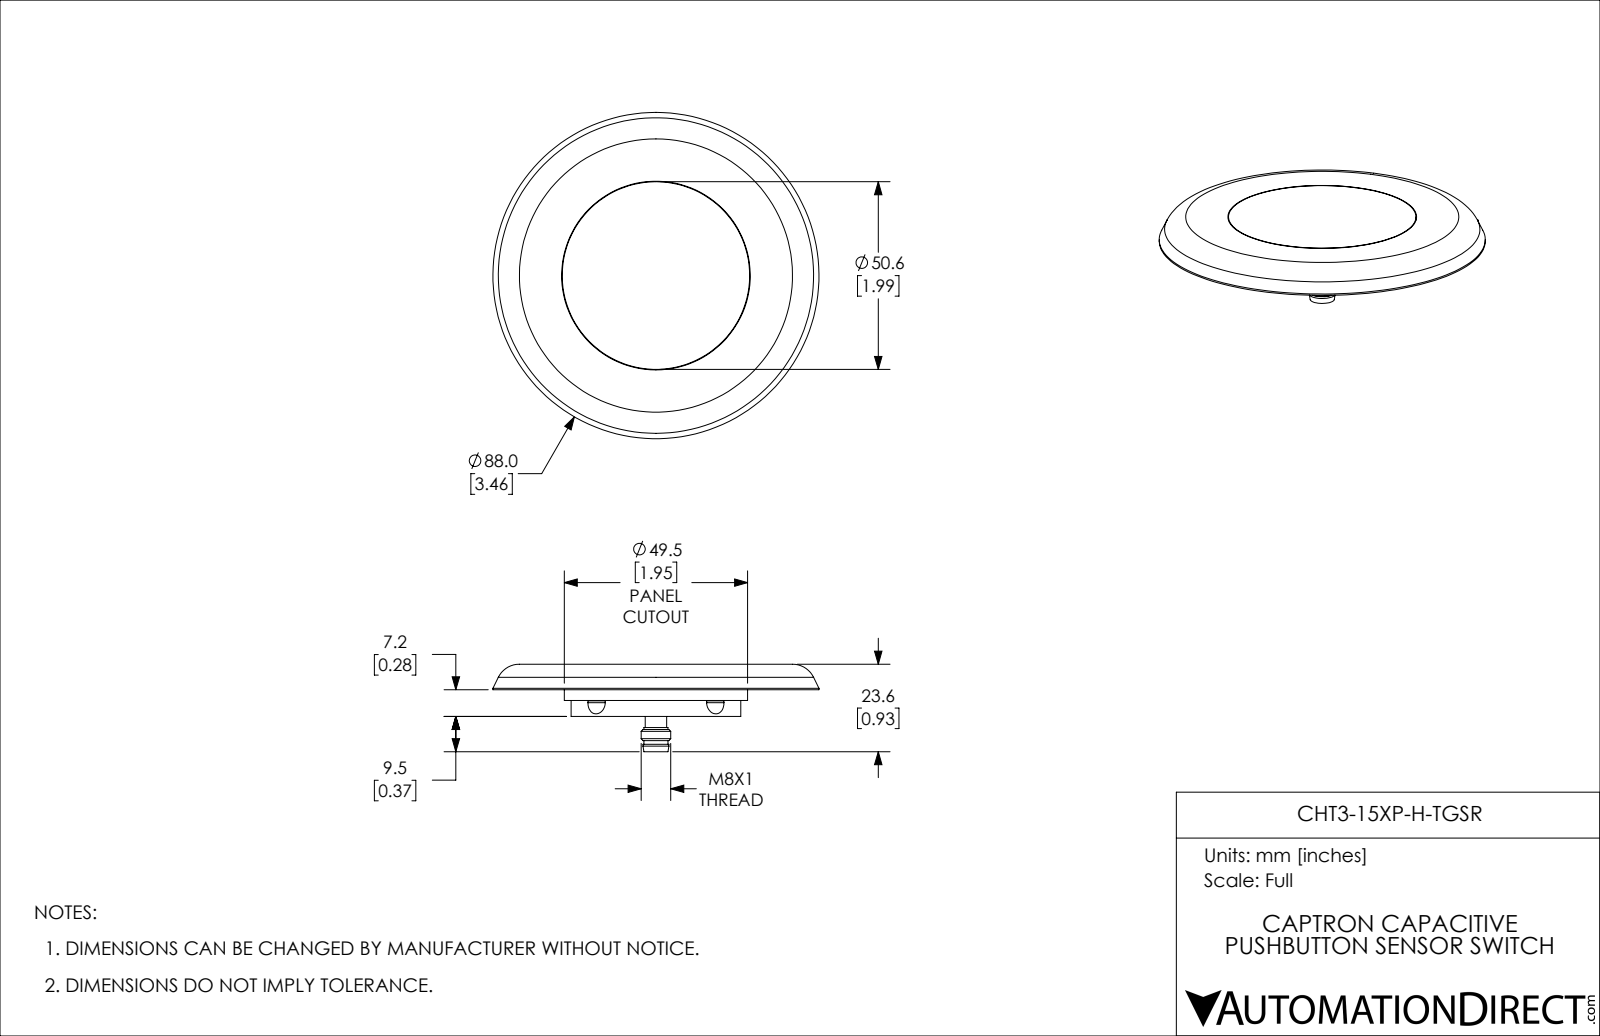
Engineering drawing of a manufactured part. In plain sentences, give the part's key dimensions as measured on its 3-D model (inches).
The part is named "CHT3-15XP-H-TGSR". Its 3-D file was written by "SolidWorks 2019 (CONFIG_CONTROL_DESIGN)". It is 9 solids with 87 faces: 25 planar, 36 cylindrical and 26 other. Overall it measures 3.465 by 3.465 by 0.929 inches. Its volume is 3.031 cubic inches and its surface area 33.39 square inches. Round holes: 1 of diameter 0.236, 1 of diameter 1.815, 1 of diameter 2.004. Round bosses or shafts: 4 of diameter 0.039, 1 of diameter 1.992, 1 of diameter 1.948, 1 of diameter 1.803, 1 of diameter 0.315, 1 of diameter 0.276, 1 of diameter 0.256, 1 of diameter 0.228. Partial cylindrical surfaces (rounded edges, fillets, slot ends): 4 of radius 0.197, 1 of radius 0.035. The main face-to-face distances are 0.272, 0.181, 0.091, 0.283, 0.465, 0.555, 0.02, 0.295, 0.303, 0.169.
